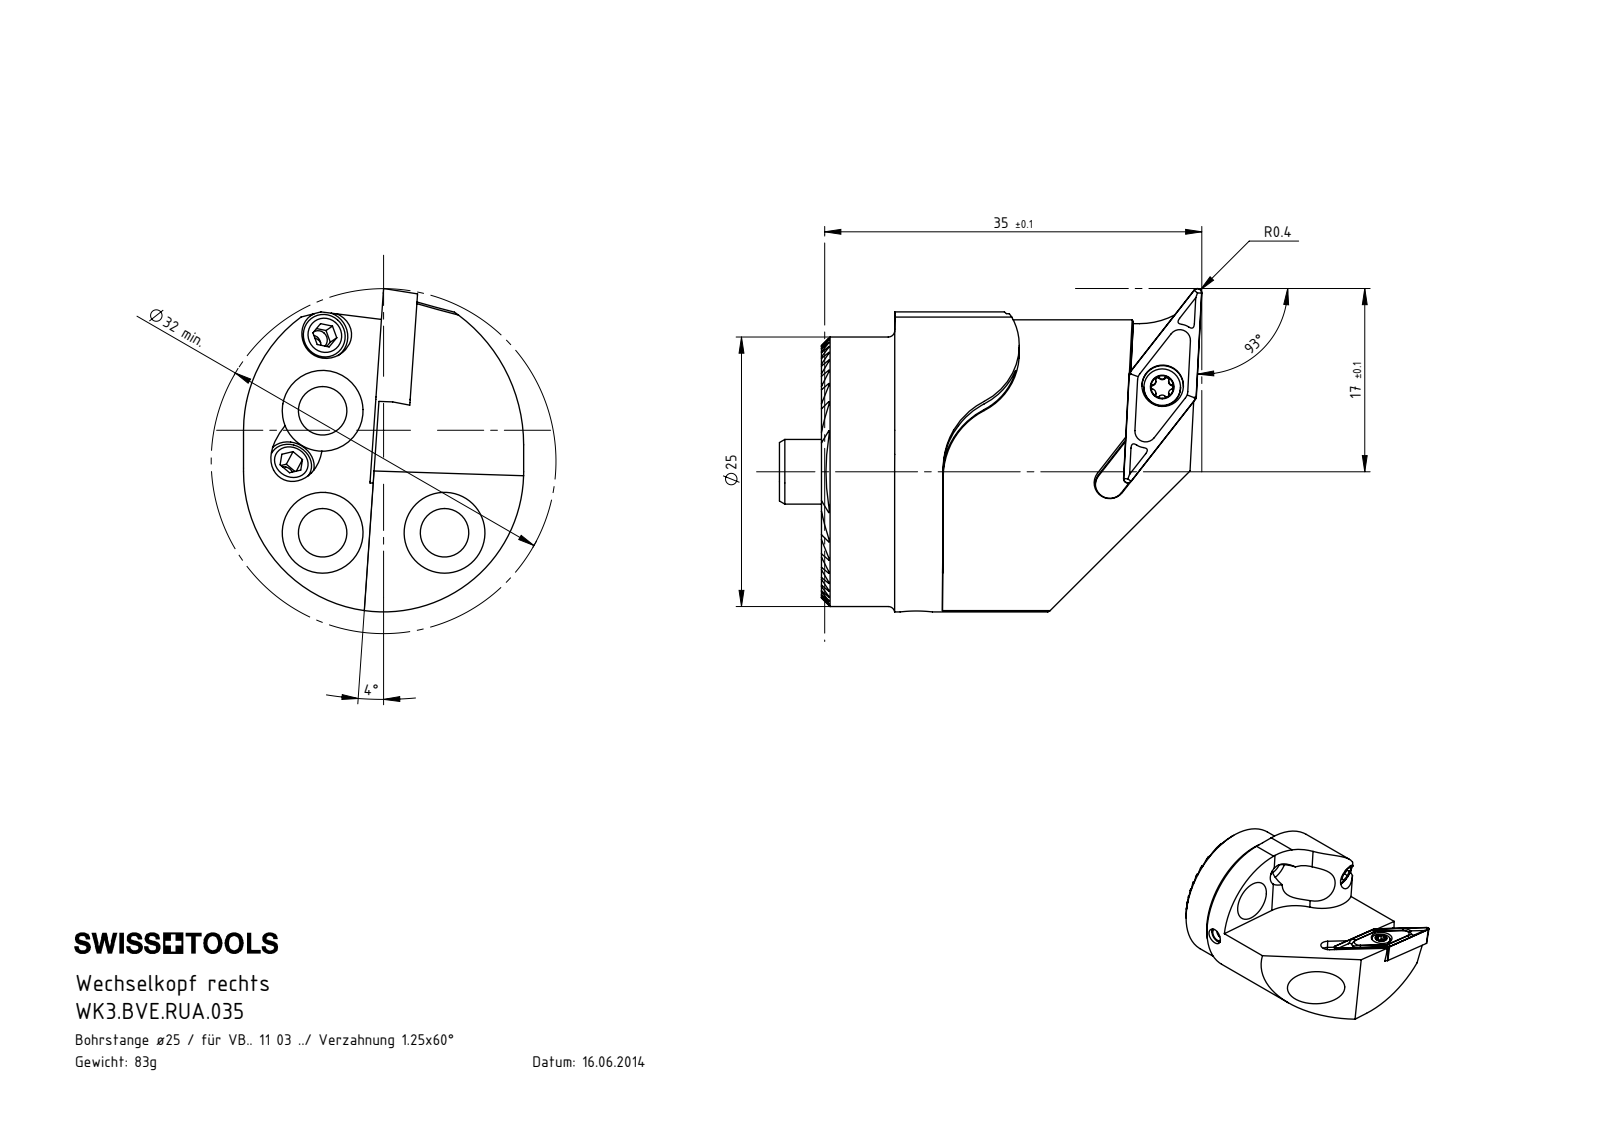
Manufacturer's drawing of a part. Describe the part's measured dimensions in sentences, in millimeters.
The part is named "VBMT110304; WKX-ER1.004.005_A_PreviewCfg; WK3-BVE.RUA.035_A_Fertigbearbeitung; KVT_MB_600_030 (+3 more)". Its 3-D file was written by "SolidWorks 2017 (AUTOMOTIVE_DESIGN)". It is 12 solids with 522 faces: 178 planar, 175 cylindrical and 169 other. Overall it measures 39.2 by 30 by 26 millimeters. Its volume is 10 401 cubic millimeters and its surface area 6 615 square millimeters. Round holes: 5 of diameter 4.5, 3 of diameter 2.38, 3 of diameter 2.5, 3 of diameter 7.5, 2 of diameter 1.7, 2 of diameter 3, 2 of diameter 3.3, 1 of diameter 2.05, 1 of diameter 2.8, 1 of diameter 3.85, 1 of diameter 4.2, 1 of diameter 6. Round bosses or shafts: 3 of diameter 3, 2 of diameter 4, 1 of diameter 25, 1 of diameter 3.4, 1 of diameter 2.5. Partial cylindrical surfaces (rounded edges, fillets, slot ends): 20 of radius 0.12, 6 of radius 0.21, 5 of radius 0.36, 2 of radius 7, 2 of radius 13, 1 of radius 0.36, 1 of radius 1.35, 1 of radius 6. The main face-to-face distances are 4.33, 1.08, 3.25, 5.41, 8.66, 7.58, 2.16, 2.17, 9.74, 6.5. The hole center spacings are 8, 11.32, 16.01.
